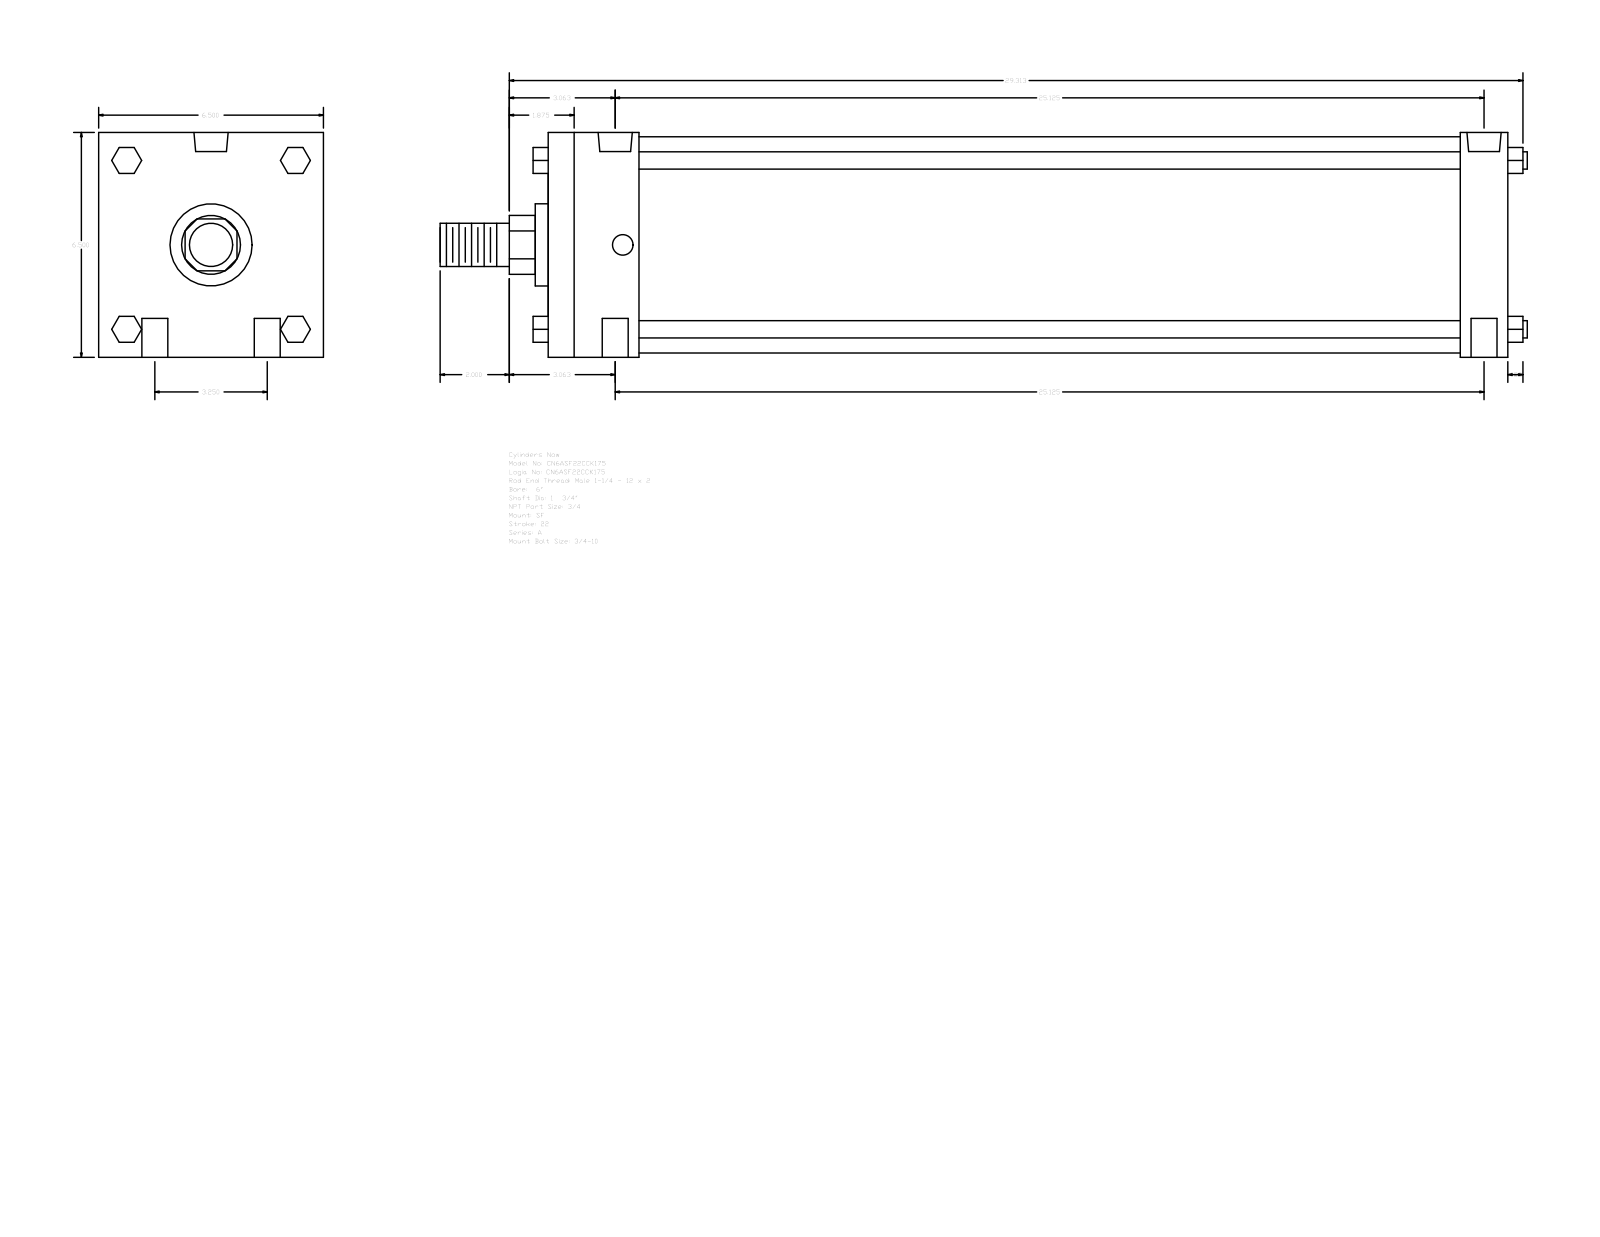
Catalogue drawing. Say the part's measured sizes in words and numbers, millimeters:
The part is named "A_SF__0600_1.75". Its 3-D file was written by "GSSL Pune (CONFIG_CONTROL_DESIGN)". It is 0 solids with 124 faces: 94 planar, 30 cylindrical and 0 other. Overall it measures 798.51 by 165.1 by 165.1 millimeters. Round holes: 4 of diameter 19.05, 2 of diameter 15.08, 2 of diameter 25.12. Round bosses or shafts: 4 of diameter 12.7, 1 of diameter 158.75, 1 of diameter 60.33, 1 of diameter 44.45, 1 of diameter 31.75. Partial cylindrical surfaces (rounded edges, fillets, slot ends): 1 of radius 21.63. The main face-to-face distances are 165.1, 704.85, 66.68, 669.93, 34.92, 603.25, 638.17, 19.05, 61.97, 107.34. The hole center spacings are 41.27, 639.5, 638.17, 82.54, 643.49, 627.05.
